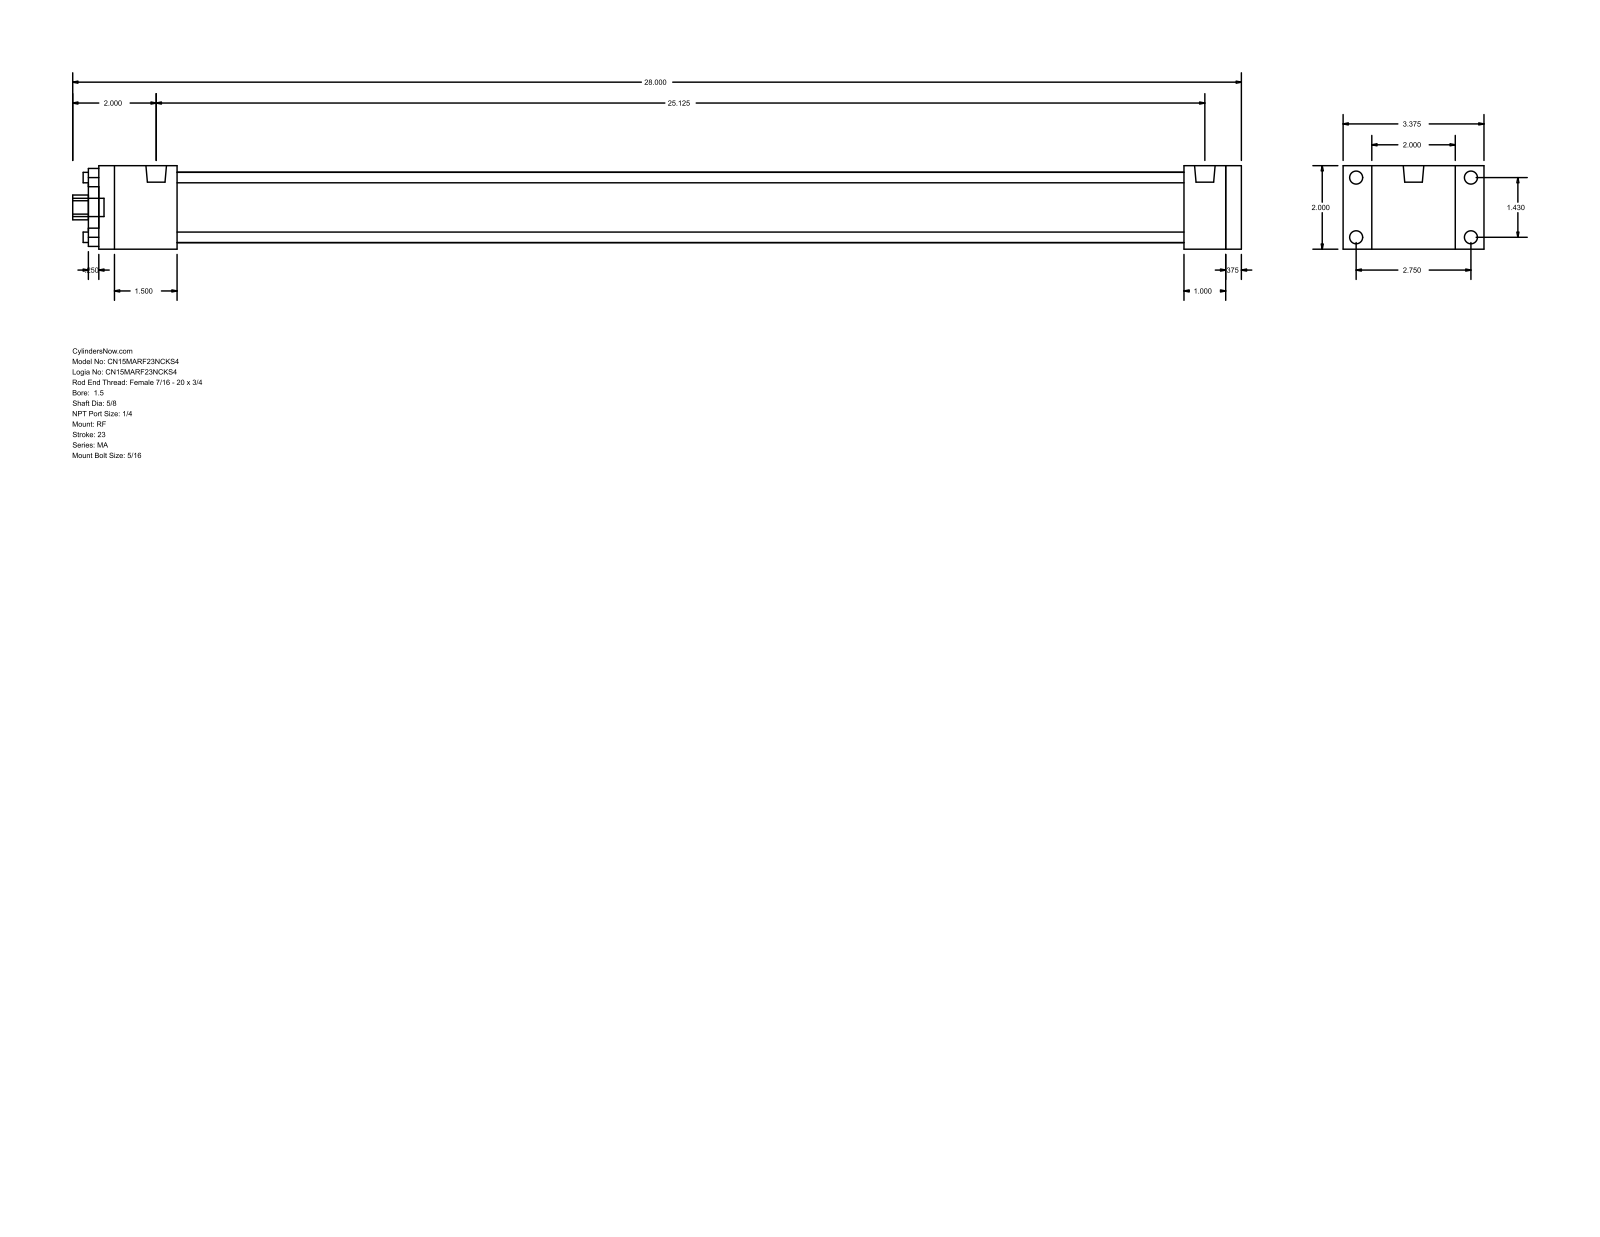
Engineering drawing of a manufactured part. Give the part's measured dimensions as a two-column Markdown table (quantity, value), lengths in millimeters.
| quantity | value |
| --- | --- |
| part name | MA_RF__0150_0.625 |
| STEP written by | GSSL Pune (CONFIG_CONTROL_DESIGN) |
| units | millimeters |
| bodies | 0 solids, 92 faces (64 planar, 28 cylindrical, 0 other) |
| overall size | 711.2 × 85.72 × 50.8 |
| round holes (diameter × count) | 6.35 × 4, 15.88 × 1, 28.57 × 1, 42.93 × 1 |
| round bosses / shafts (diameter × count) | 7.94 × 8, 12.49 × 2, 11.11 × 1 |
| partial cylindrical surfaces (radius × count) | 7.54 × 1 |
| main face-to-face distances | 50.8, 9.53, 695.32, 685.79, 660.39, 25.4, 34.93, 47.62, 612.77, 638.17 |
| hole center spacings | 25.68, 36.32, 51.36 |
